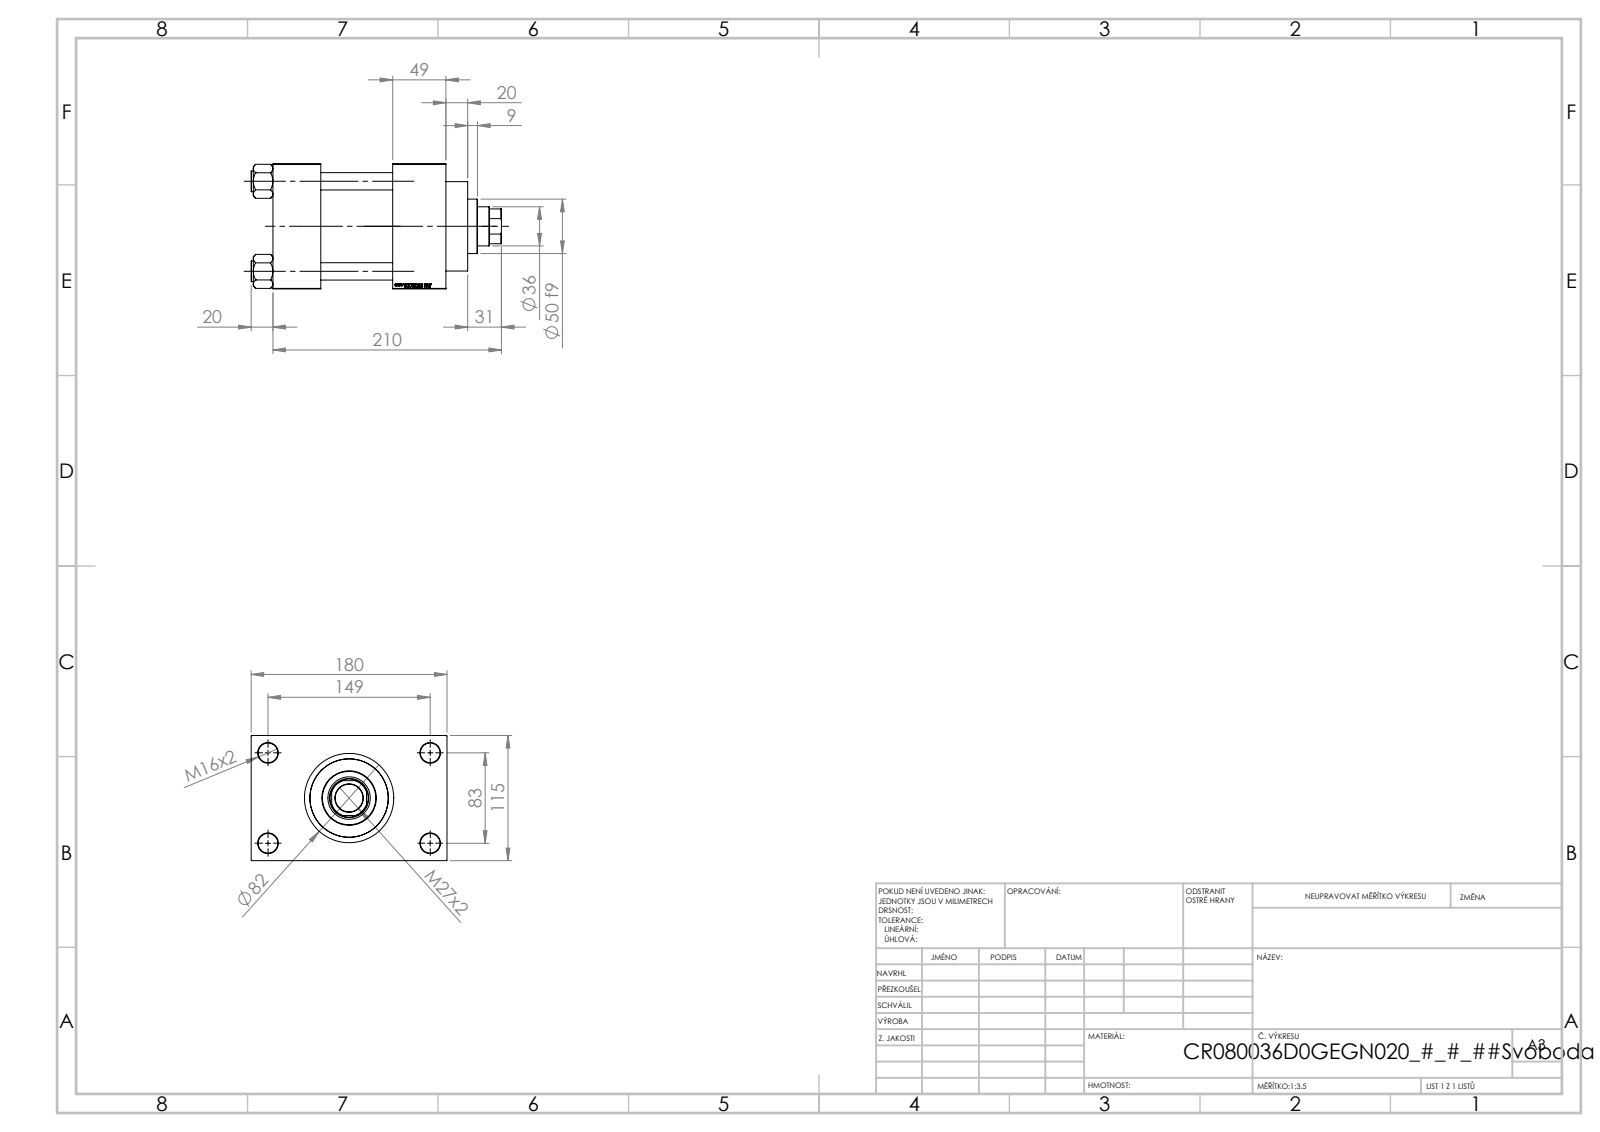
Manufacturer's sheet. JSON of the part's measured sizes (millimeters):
{"part_name": "NUT_M5_D; V215_VC_A; V215CR_VCP_D; V215CR_D_TYCINKA (+1 more)", "step_written_by": "SolidWorks 2019 (CONFIG_CONTROL_DESIGN)", "units": "millimeters", "bodies": {"solids": 11, "faces": 1152, "planar": 545, "cylindrical": 89, "other": 518}, "overall_size": [230, 180, 115], "volume_mm3": 1997000, "surface_area_mm2": 293897, "round_holes": [[16, 4], [18, 4], [7, 2], [26.44, 2], [35, 2], [25.5, 1], [36, 1], [39, 1], [61, 1], [72, 1], [80, 1]], "round_bosses_or_shafts": [[19, 4], [86, 1], [82, 1], [50, 1]], "partial_cylinders_radius": [[17.5, 1]], "face_to_face_distances": [115, 66, 110, 49, 44, 159, 32.5, 147.5, 20, 69], "hole_center_spacings": [33.15, 58.48, 82.7, 85.28, 89.24, 115.85, 142.43, 83]}
